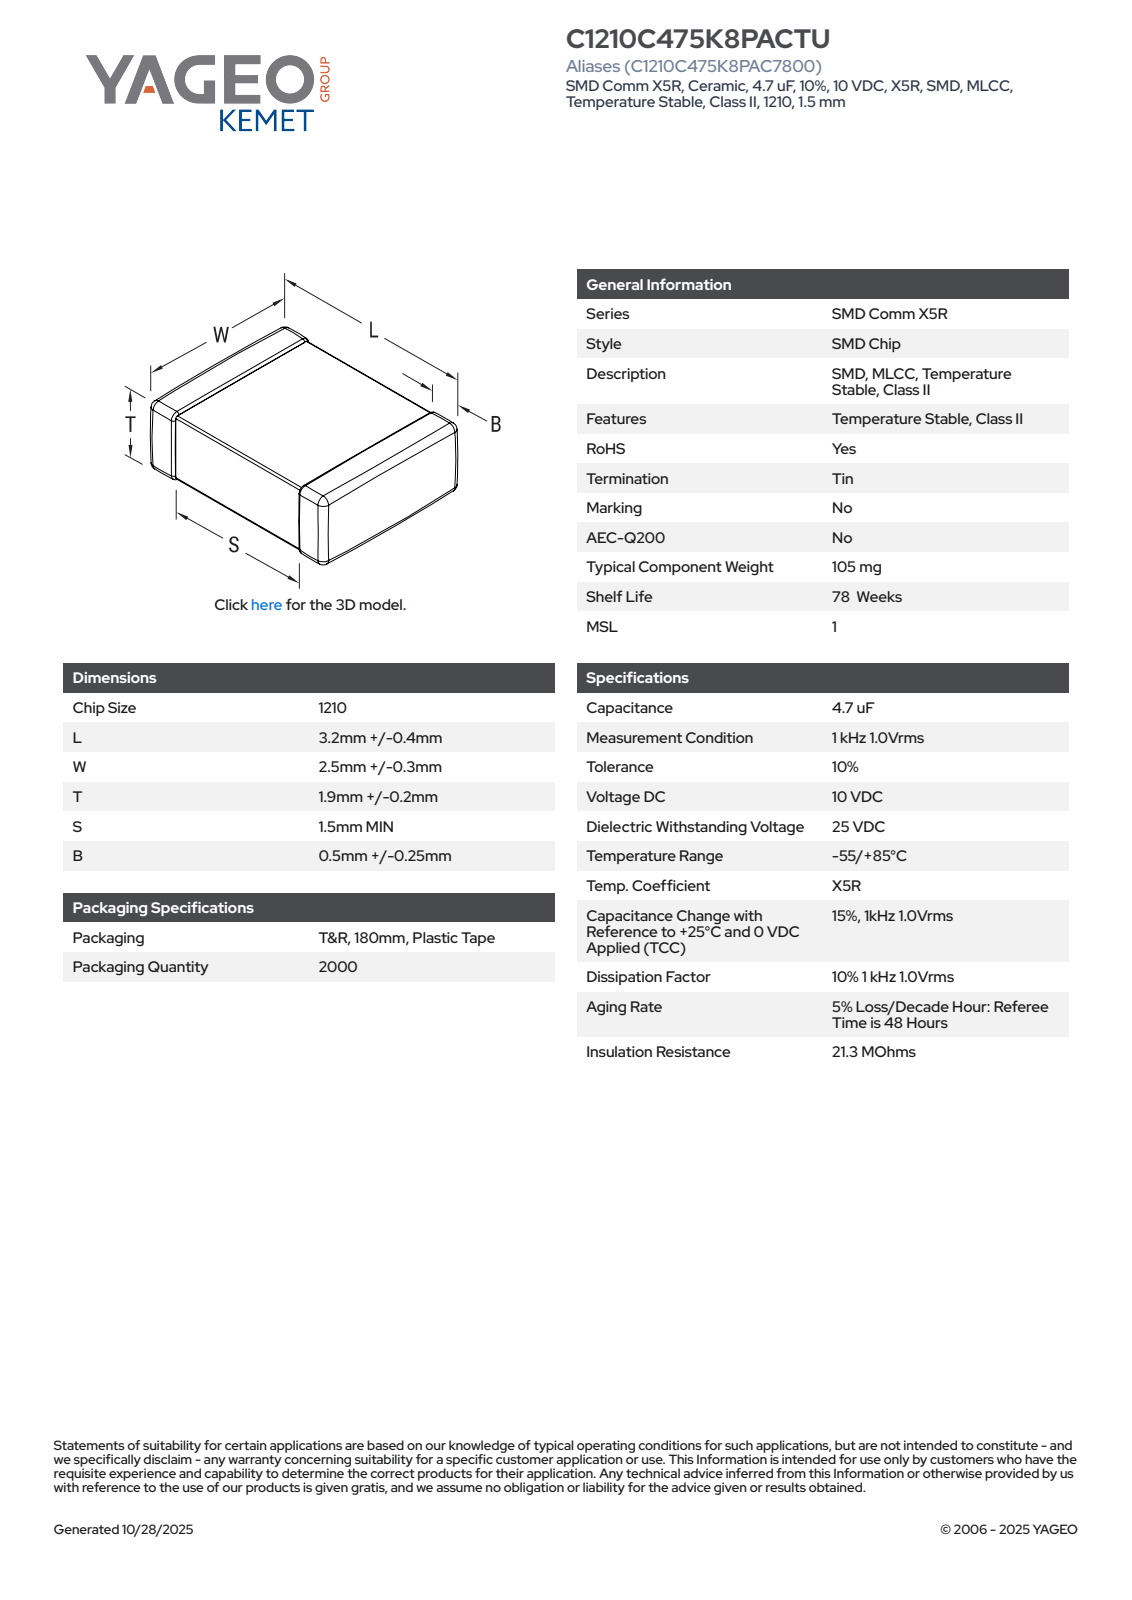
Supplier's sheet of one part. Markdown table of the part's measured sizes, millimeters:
| quantity | value |
| --- | --- |
| part name | CCS_CCSTD_1210_L3.6W2.8T2.1B0.5 |
| STEP written by | SolidWorks 2021 (AUTOMOTIVE_DESIGN) |
| units | millimeters |
| bodies | 4 solids, 125 faces (71 planar, 38 cylindrical, 16 other) |
| overall size | 3.6 × 2.8 × 2.1 |
| volume | 20 mm³ |
| surface area | 47 mm² |
| main face-to-face distances | 2.04, 1.98, 3.6, 2.74, 2.68, 2.1, 2.8, 1.99, 2.05, 1.53 |
